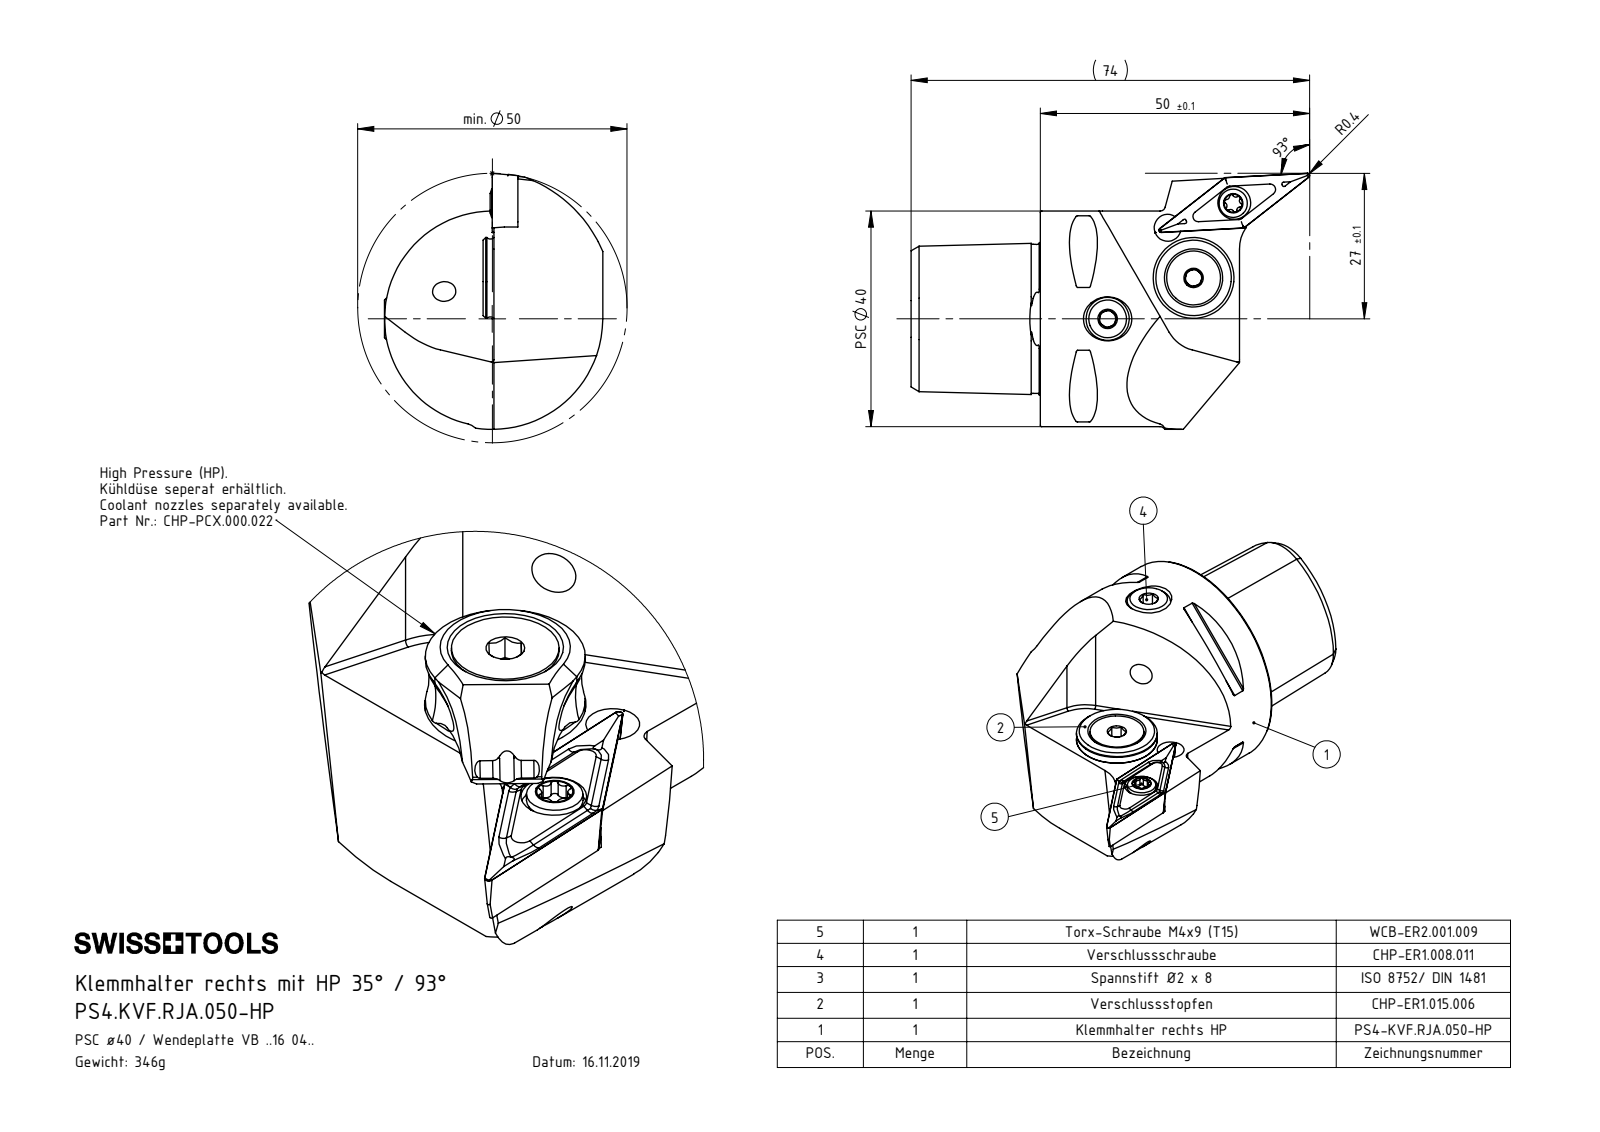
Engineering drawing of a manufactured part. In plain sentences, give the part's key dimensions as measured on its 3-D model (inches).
The part is named "PS4.KVF.RJA.050-HP; CHP-ER1.015.006; DIN 7991 - M5x15; VBMT160404 (+6 more)". Its 3-D file was written by "SolidWorks 2017 (AUTOMOTIVE_DESIGN)". It is 8 solids with 281 faces: 93 planar, 64 cylindrical and 124 other. Overall it measures 2.913 by 1.87 by 1.594 inches. Its volume is 2.652 cubic inches and its surface area 23.08 square inches. Round holes: 2 of diameter 0.13, 2 of diameter 0.165, 2 of diameter 0.197, 1 of diameter 0.047, 1 of diameter 0.079, 1 of diameter 0.098, 1 of diameter 0.118, 1 of diameter 0.157, 1 of diameter 0.173, 1 of diameter 0.181, 1 of diameter 0.205, 1 of diameter 0.24. Round bosses or shafts: 1 of diameter 1.575, 1 of diameter 0.591, 1 of diameter 0.528, 1 of diameter 0.394, 1 of diameter 0.315, 1 of diameter 0.217, 1 of diameter 0.207, 1 of diameter 0.197. Partial cylindrical surfaces (rounded edges, fillets, slot ends): 8 of radius 0.012, 6 of radius 0.013, 6 of radius 0.023, 2 of radius 0.006, 2 of radius 0.02, 2 of radius 0.276, 1 of radius 0.118, 1 of radius 0.807. The main face-to-face distances are 0.177, 0.176, 0.945, 0.618, 0.62, 0.795, 0.611, 0.591, 1.39, 0.354. The hole center spacings are 0.02, 0.177, 0.28, 0.412, 0.459, 0.466, 0.511, 0.52.
